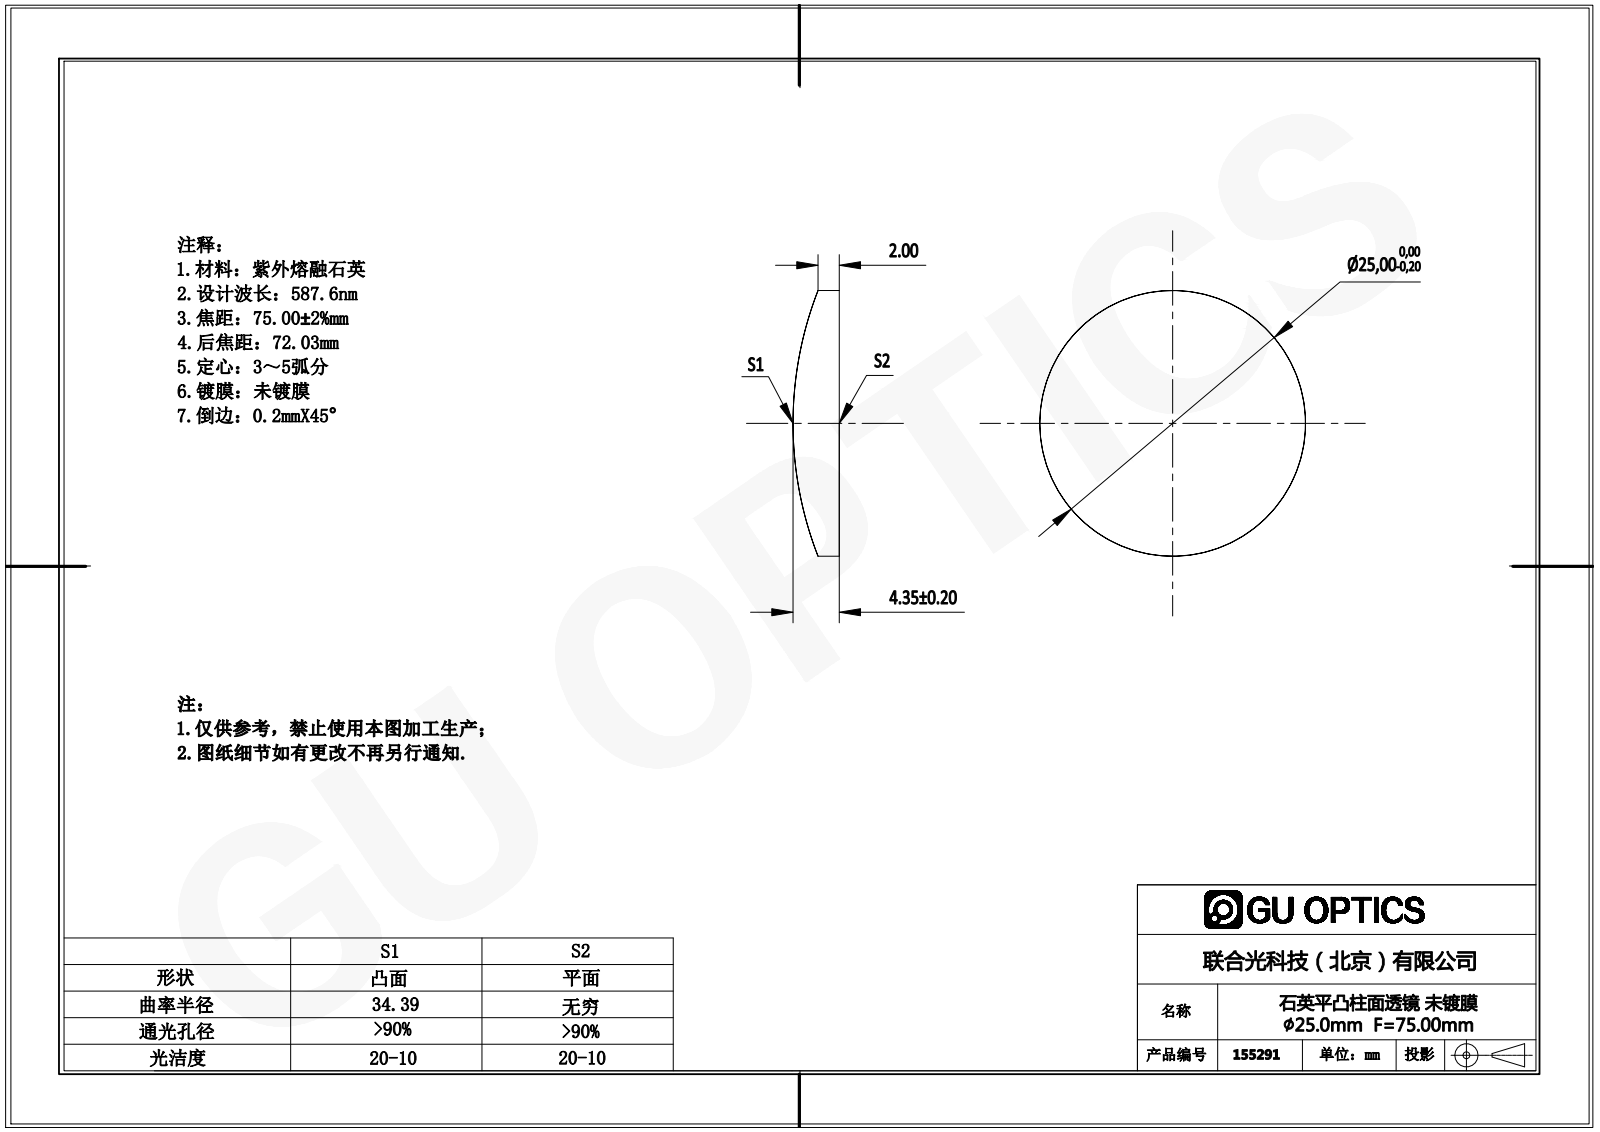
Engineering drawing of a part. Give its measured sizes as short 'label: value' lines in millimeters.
name: 155291
written by: SolidWorks 2016 (AUTOMOTIVE_DESIGN)
unit: mm
bodies: 1 solid, 4 faces (1 planar, 3 cylindrical, 0 other)
size: 25 × 25 × 4.35
volume: 1 852 mm³; area: 1 240 mm²
bosses: 1× ⌀25
rounds: 1× R34.39
